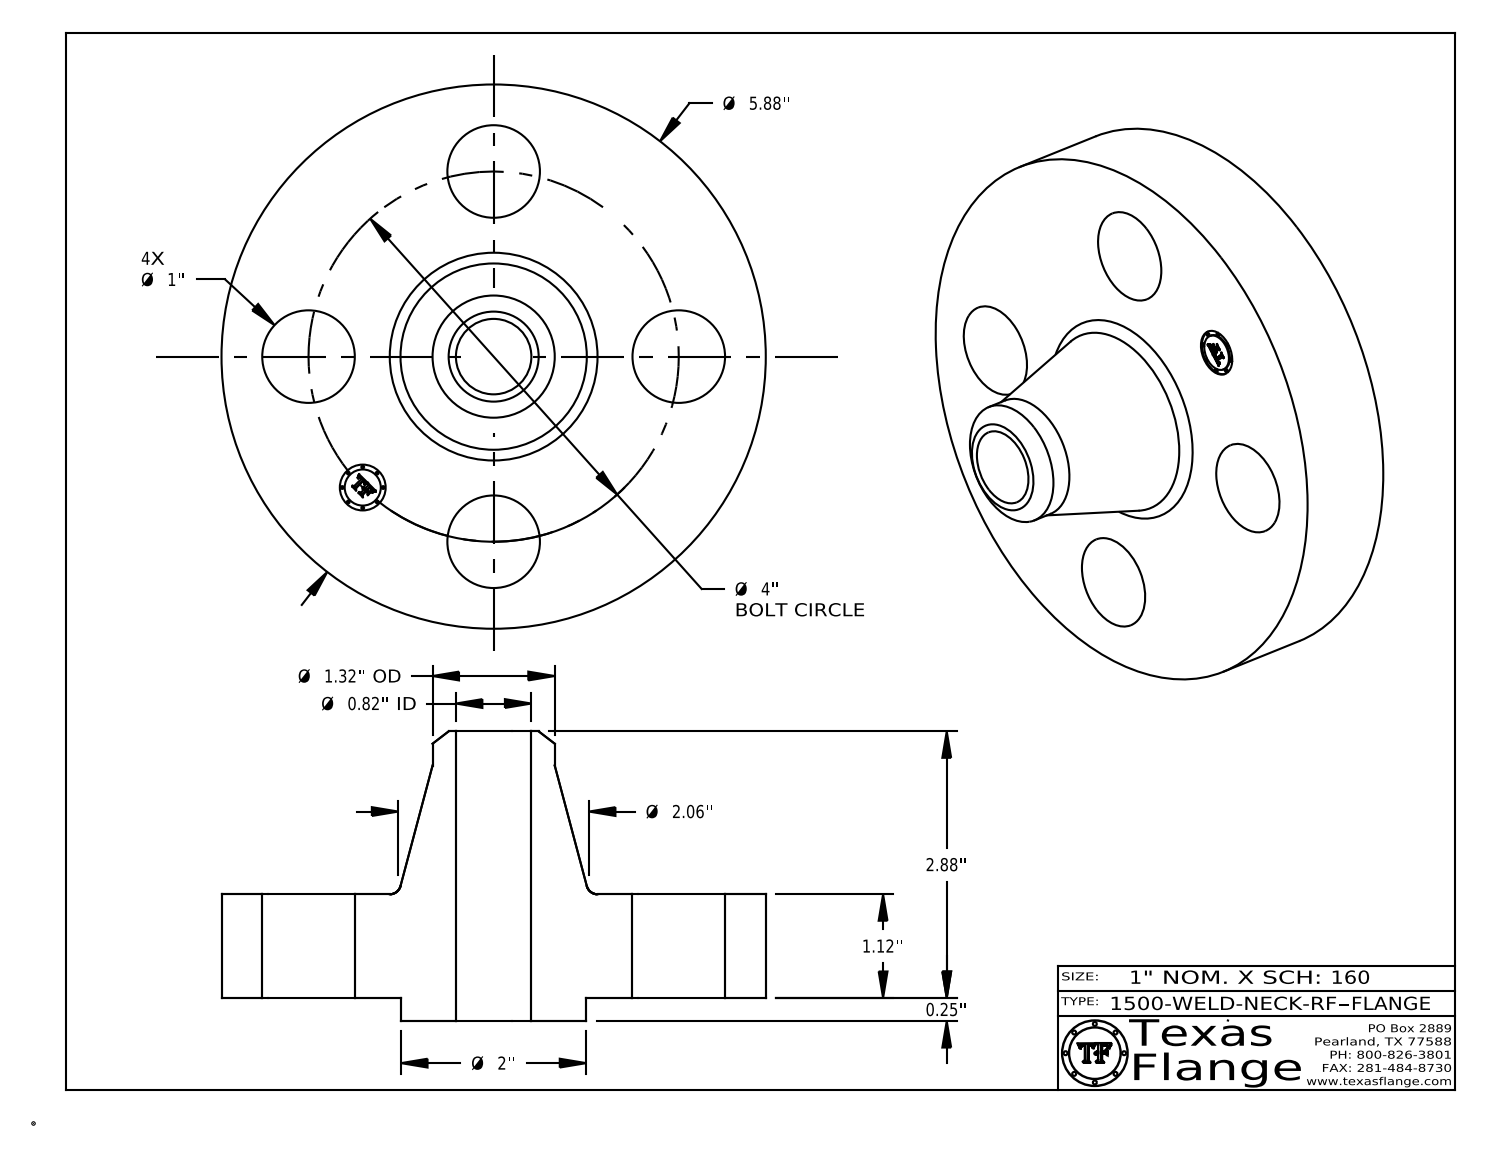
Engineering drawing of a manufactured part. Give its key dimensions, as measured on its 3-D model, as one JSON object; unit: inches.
{"part_name": "1500-WELD-NECK-RF", "step_written_by": "CATIA V5 STEP AP214 (AUTOMOTIVE_DESIGN)", "units": "inches", "bodies": {"solids": 1, "faces": 411, "planar": 369, "cylindrical": 36, "other": 6}, "overall_size": [5.88, 5.88, 3.13], "volume_in3": 29.69, "surface_area_in2": 98.07, "round_holes": [[1, 4], [0.495, 1], [0.815, 1]], "round_bosses_or_shafts": [[0.03, 8], [5.88, 1], [2, 1], [1.32, 1], [0.39, 1]], "face_to_face_distances": [1.12, 0.25, 1.37, 3.13, 2.88, 1.76, 0.015, 1.355, 1.105, 1.775], "hole_center_spacings": [2, 2.828, 1.531, 3.695, 4]}
